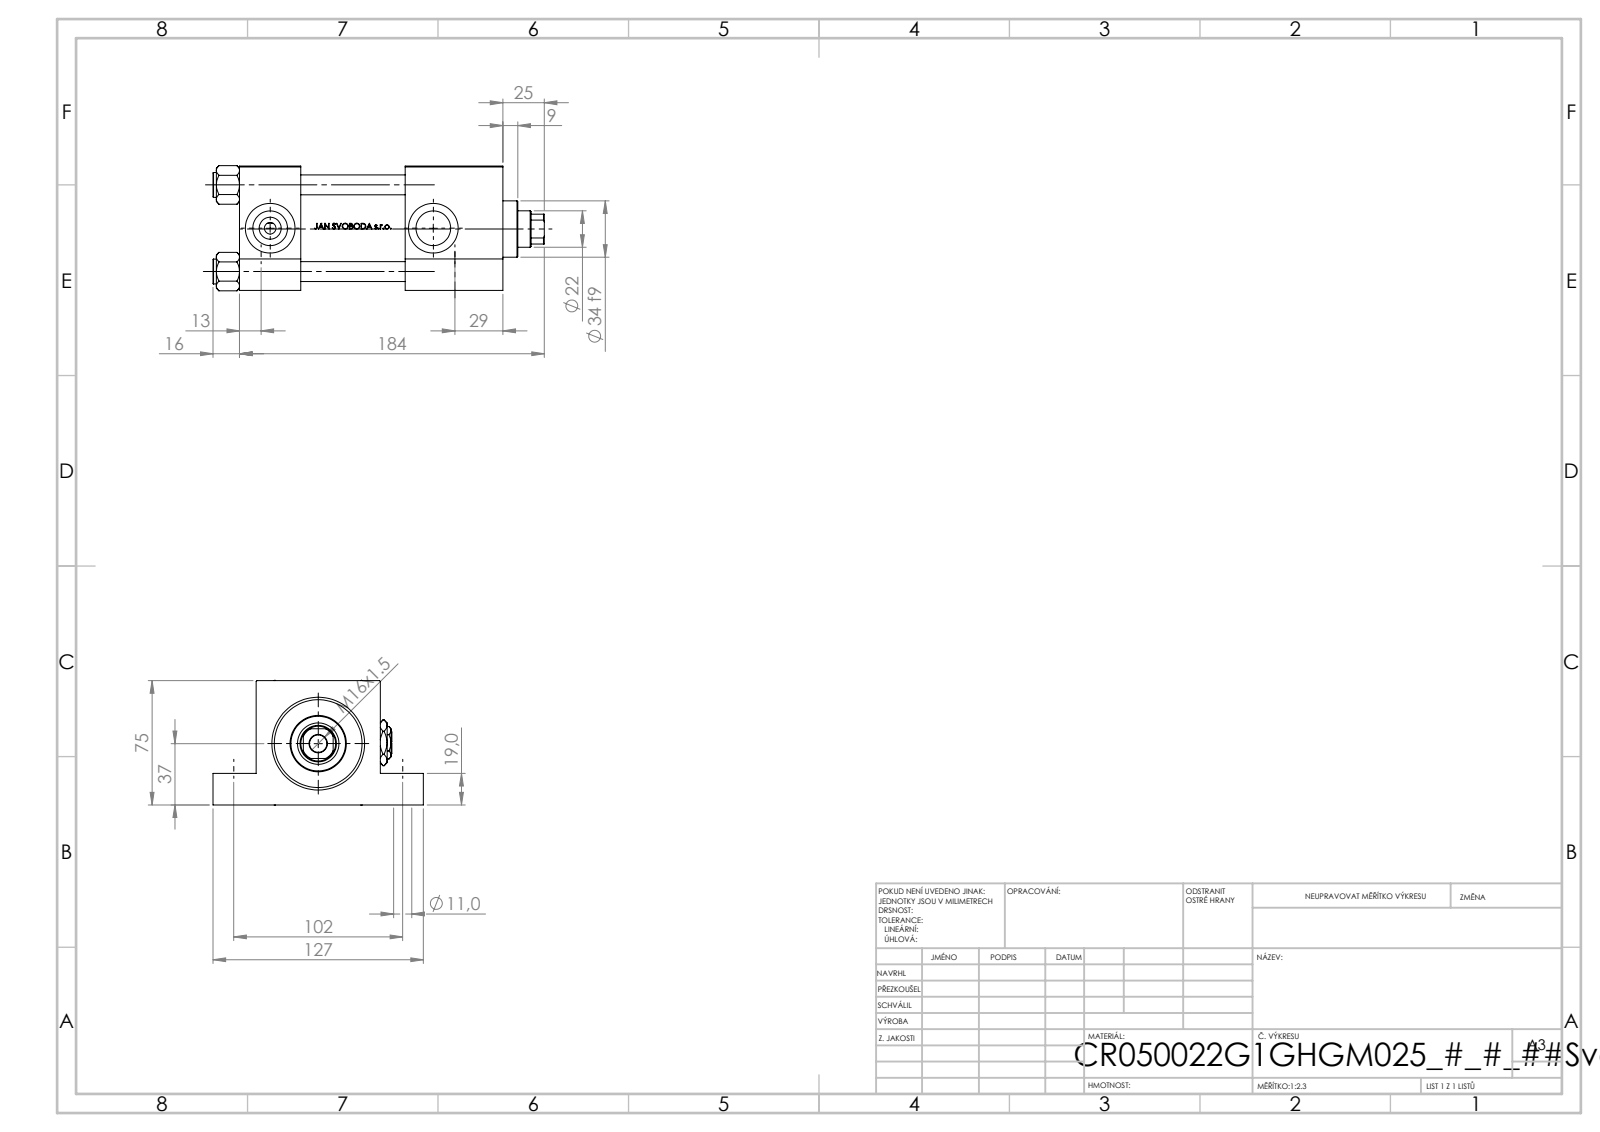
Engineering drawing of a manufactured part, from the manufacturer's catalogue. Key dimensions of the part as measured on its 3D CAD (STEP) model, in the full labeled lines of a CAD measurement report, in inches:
Part name (STEP PRODUCT): NUT_M5_G; V215CR_G_TYCINKA; V215CR_VCP_G; V215CR_G_Body (+2 more)
STEP written by: SolidWorks 2019 (CONFIG_CONTROL_DESIGN)
Units: inches
Bodies: 12 solids, 1134 faces (454 planar, 128 cylindrical, 552 other)
Overall size (bounding box): 7.874 × 5 × 2.974
Volume: 46.32 in³ · Surface area: 254.3 in²
Round holes (diameter × count): ⌀0.433 ×4, ⌀0.472 ×4, ⌀0.276 ×2, ⌀0.825 ×2, ⌀1.181 ×2, ⌀0.413 ×1, ⌀0.866 ×1, ⌀0.984 ×1, ⌀1.614 ×1, ⌀1.969 ×1, ⌀2.087 ×1
Round bosses / shafts (diameter × count): ⌀0.591 ×4, ⌀2.205 ×1, ⌀1.339 ×1
Partial cylindrical surfaces — rounded edges, fillets, slot ends (radius × count): R0.413 ×1
Main face-to-face distances: 2.953, 1.457, 6.26, 4.803, 0.748, 2.205, 2.48, 3.937, 2.323, 1.024
Hole centre spacings: 2.059, 1.442, 1.47, 2.912, 4.016, 4.606, 6.111, 3.878
